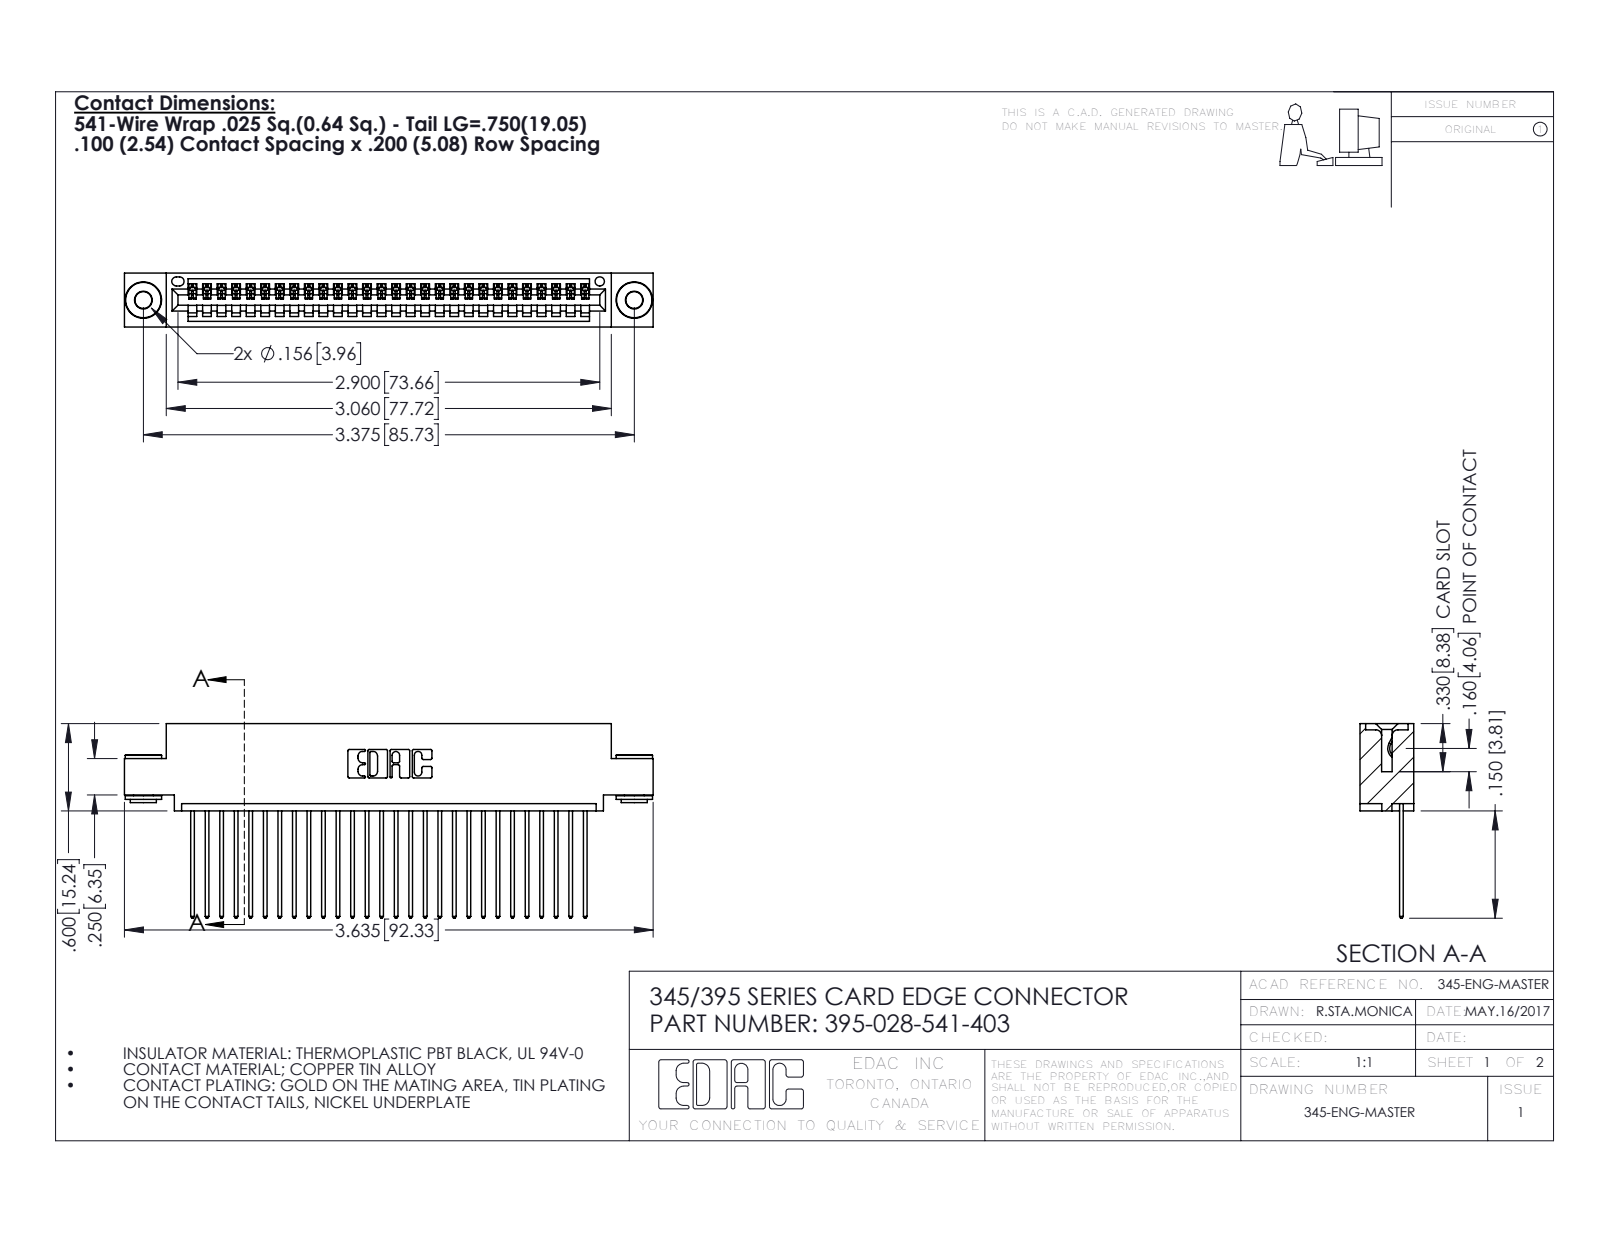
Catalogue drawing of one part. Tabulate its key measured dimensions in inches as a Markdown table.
| quantity | value |
| --- | --- |
| part name | 395-028-541-403; 345-292-001_345-293-141; 345-250-002_345-250-002-102; 345 Part_0.110 Offset - 0.156 Dia-TH |
| STEP written by | SolidWorks 2016 (CONFIG_CONTROL_DESIGN) |
| units | inches |
| bodies | 31 solids, 1792 faces (1214 planar, 570 cylindrical, 8 other) |
| overall size | 3.635 × 1.337 × 0.37 |
| volume | 0.53 in³ |
| surface area | 18.91 in² |
| round holes (diameter × count) | 0.116 × 2, 0.156 × 2, 0.064 × 1 |
| round bosses / shafts (diameter × count) | 0.25 × 2, 0.18 × 2, 0.136 × 2 |
| partial cylindrical surfaces (radius × count) | 0.006 × 56, 0.01 × 56, 0.01 × 22, 0.007 × 6, 0.031 × 6, 0.026 × 3, 0.031 × 2, 0.04 × 2 |
| main face-to-face distances | 0.072, 0.298, 0.025, 0.37, 0.098, 0.272, 0.2, 0.225, 0.149, 0.072 |
| hole center spacings | 0.27, 3.14, 3.375 |
